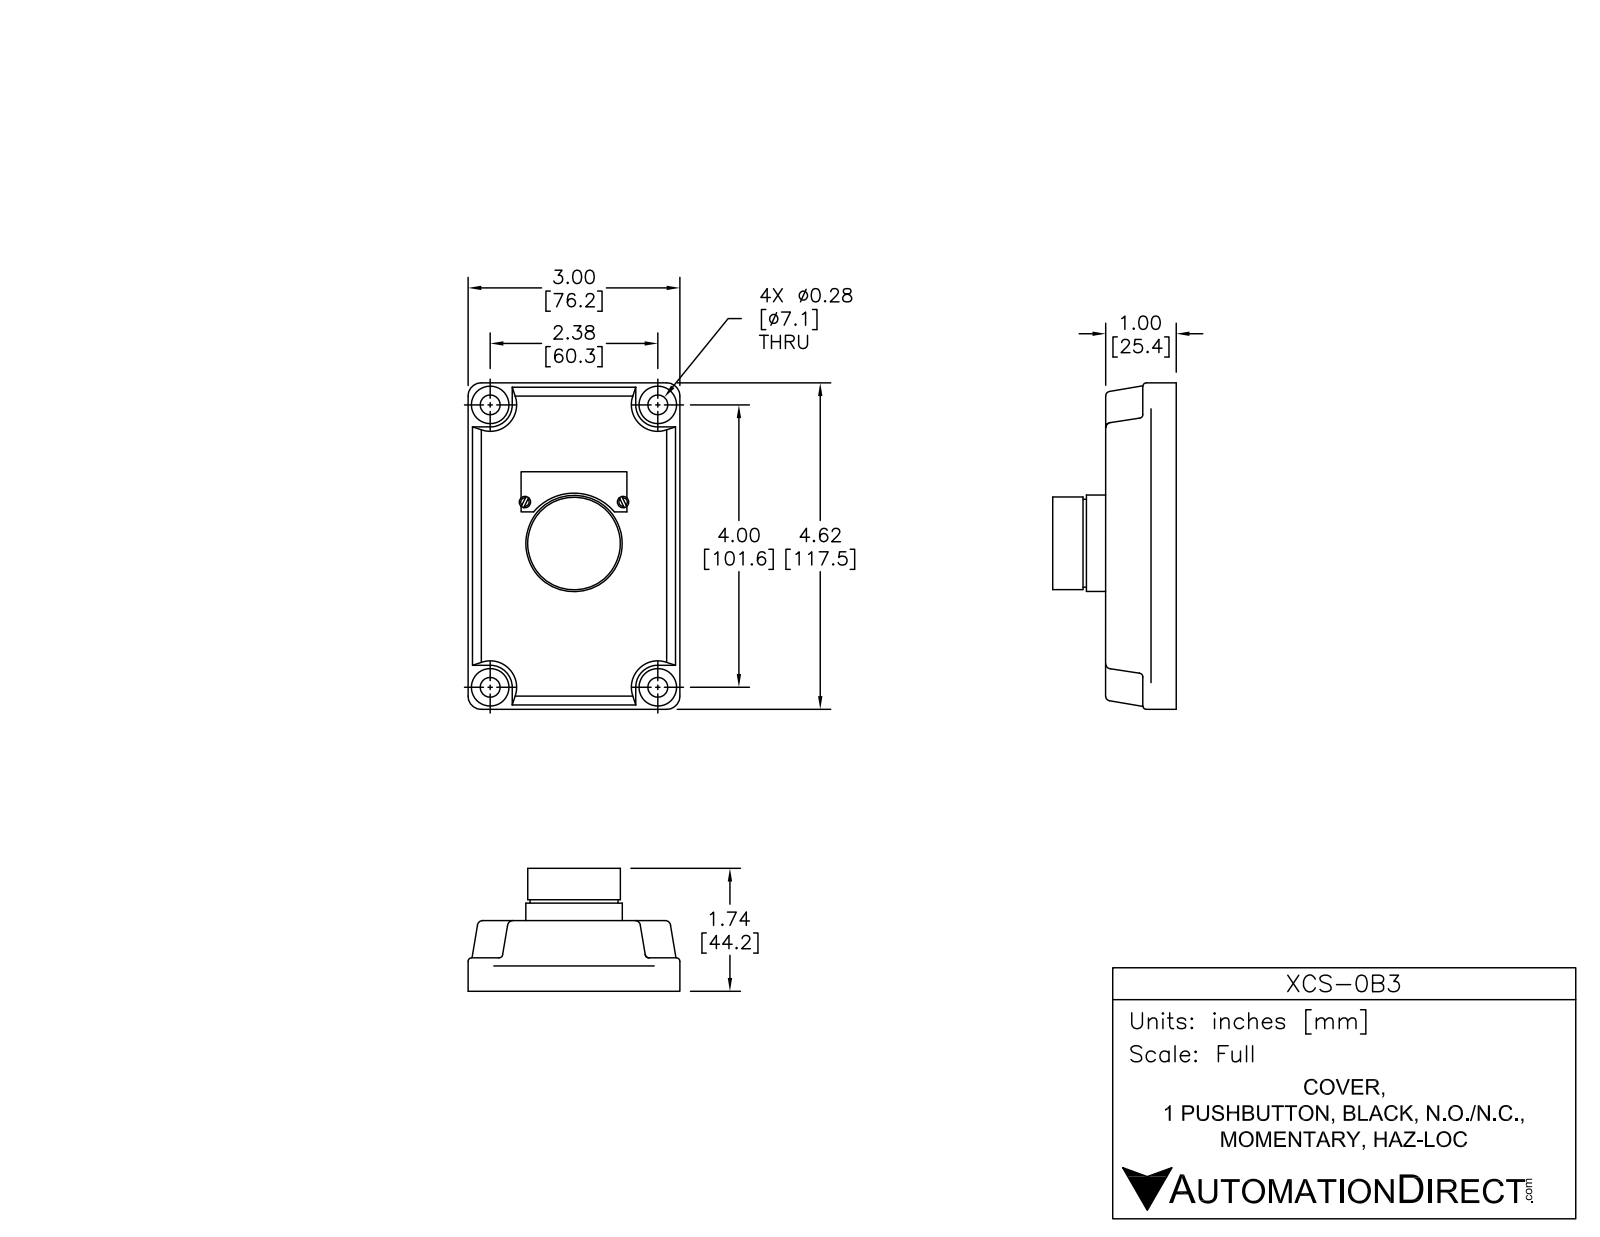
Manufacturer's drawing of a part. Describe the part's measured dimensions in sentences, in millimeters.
The part is named "XCS-0B3". Its 3-D file was written by "SolidWorks 2015 (AUTOMOTIVE_DESIGN)". It is 10 solids with 470 faces: 166 planar, 171 cylindrical and 133 other. Overall it measures 117.6 by 81.1 by 78.74 millimeters. Its volume is 207 620 cubic millimeters and its surface area 55 537 square millimeters. Round holes: 4 of diameter 6.65, 4 of diameter 6.86, 1 of diameter 28.5. Round bosses or shafts: 6 of diameter 3.3, 4 of diameter 11.6, 4 of diameter 6.35, 1 of diameter 35, 1 of diameter 32.06, 1 of diameter 26.25. Partial cylindrical surfaces (rounded edges, fillets, slot ends): 28 of radius 0.25, 10 of radius 1.27, 8 of radius 0.51, 8 of radius 1.4, 8 of radius 3, 4 of radius 2.38, 4 of radius 2.54, 4 of radius 9.65. The main face-to-face distances are 13.34, 12.7, 26.04, 11.3, 24, 37.34, 17.5, 6.5, 4.8, 30.84. The hole center spacings are 59.11, 10.2, 20.4, 60.46, 101.6, 118.23, 10.13, 10.18.
